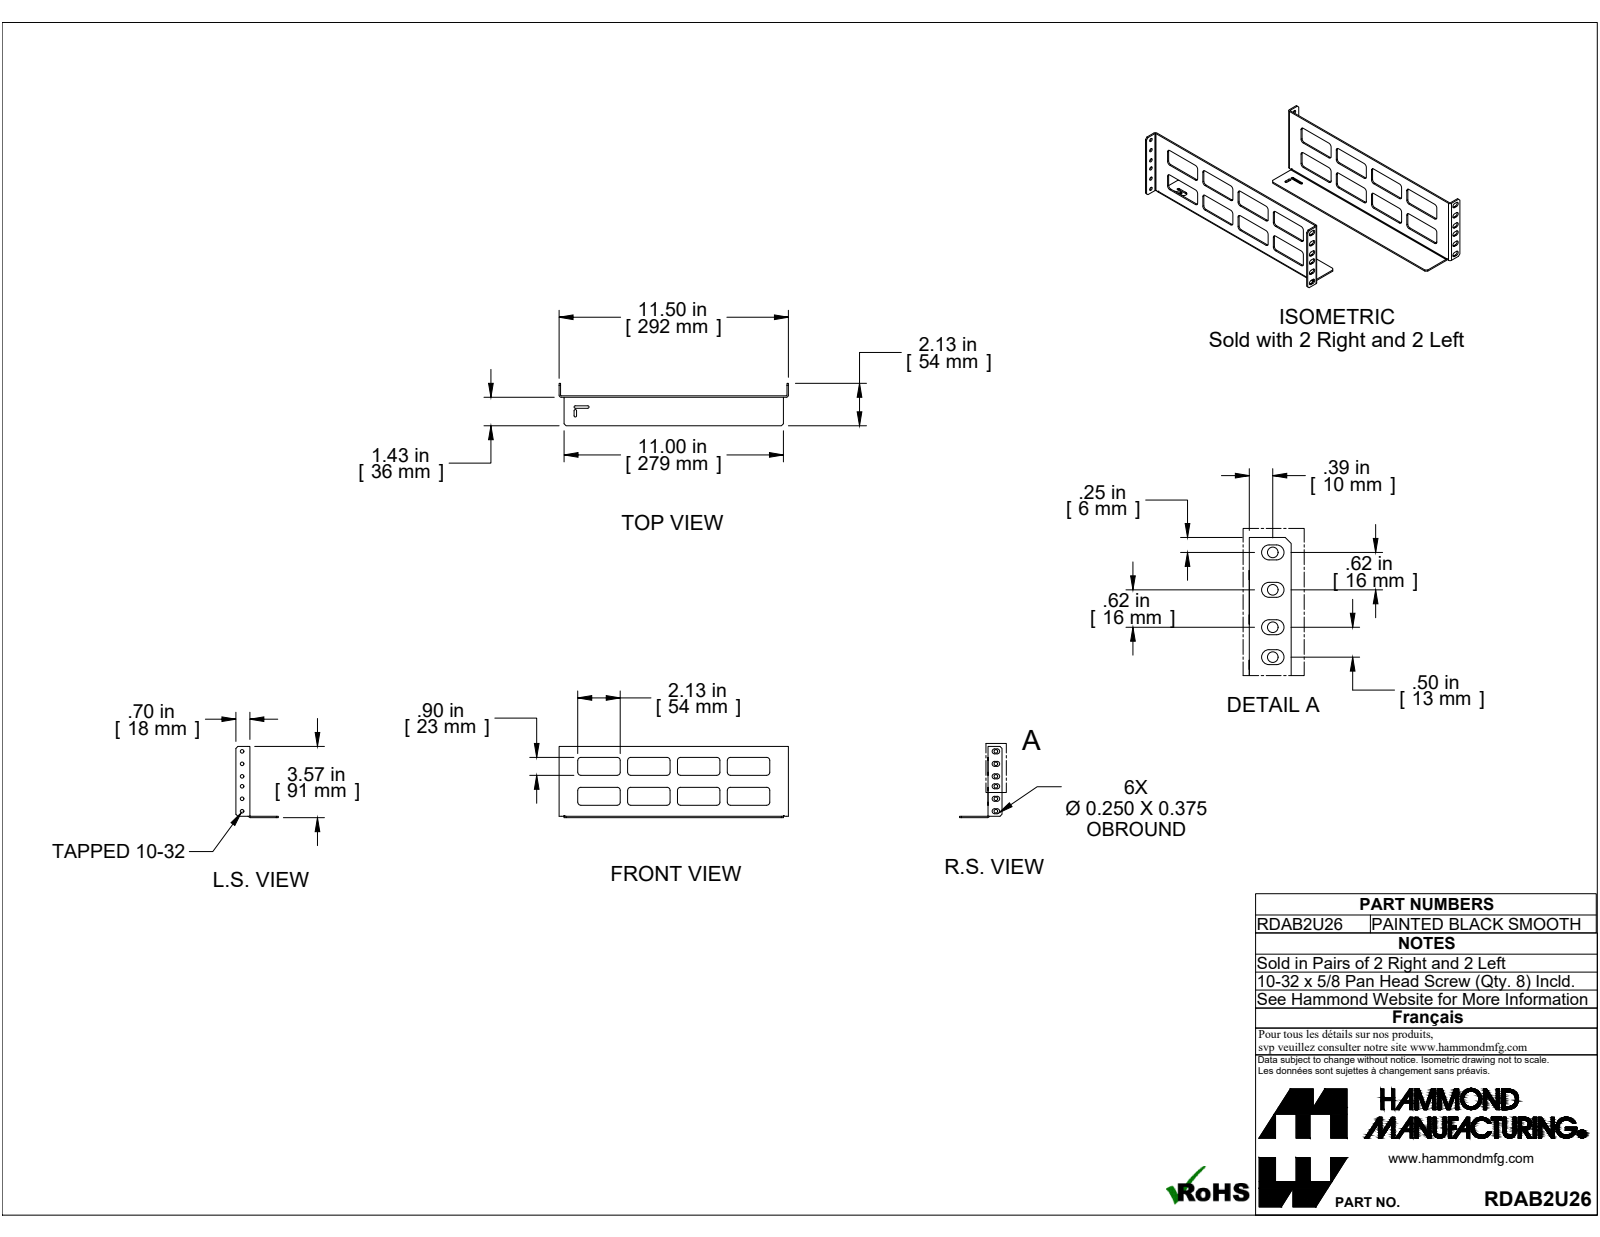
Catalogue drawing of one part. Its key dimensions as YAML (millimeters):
part_name: "RDAB2U26"
step_written_by: "SolidWorks 2019 (CONFIG_CONTROL_DESIGN)"
units: millimeters
bodies: {solids: 4, faces: 540, planar: 296, cylindrical: 244, other: 0}
overall_size: [660.4, 480.8, 90.7]
volume: 210600
surface_area: 247600
round_holes:
  - {diameter: 4.5, count: 13}
partial_cylinders:
  - {radius: 4, count: 64}
  - {radius: 3.2, count: 26}
  - {radius: 0.9, count: 10}
  - {radius: 2.7, count: 10}
  - {radius: 1.6, count: 8}
  - {radius: 1.6, count: 6}
  - {radius: 4, count: 2}
face_to_face_distances: [1.8, 447, 448.9, 445.2, 368.3, 290.3, 658.6, 38.1, 292.1, 366.5]
hole_center_spacings: [465.4, 465.1, 467.3, 44.5, 15.9, 15.9, 466, 31.8]
